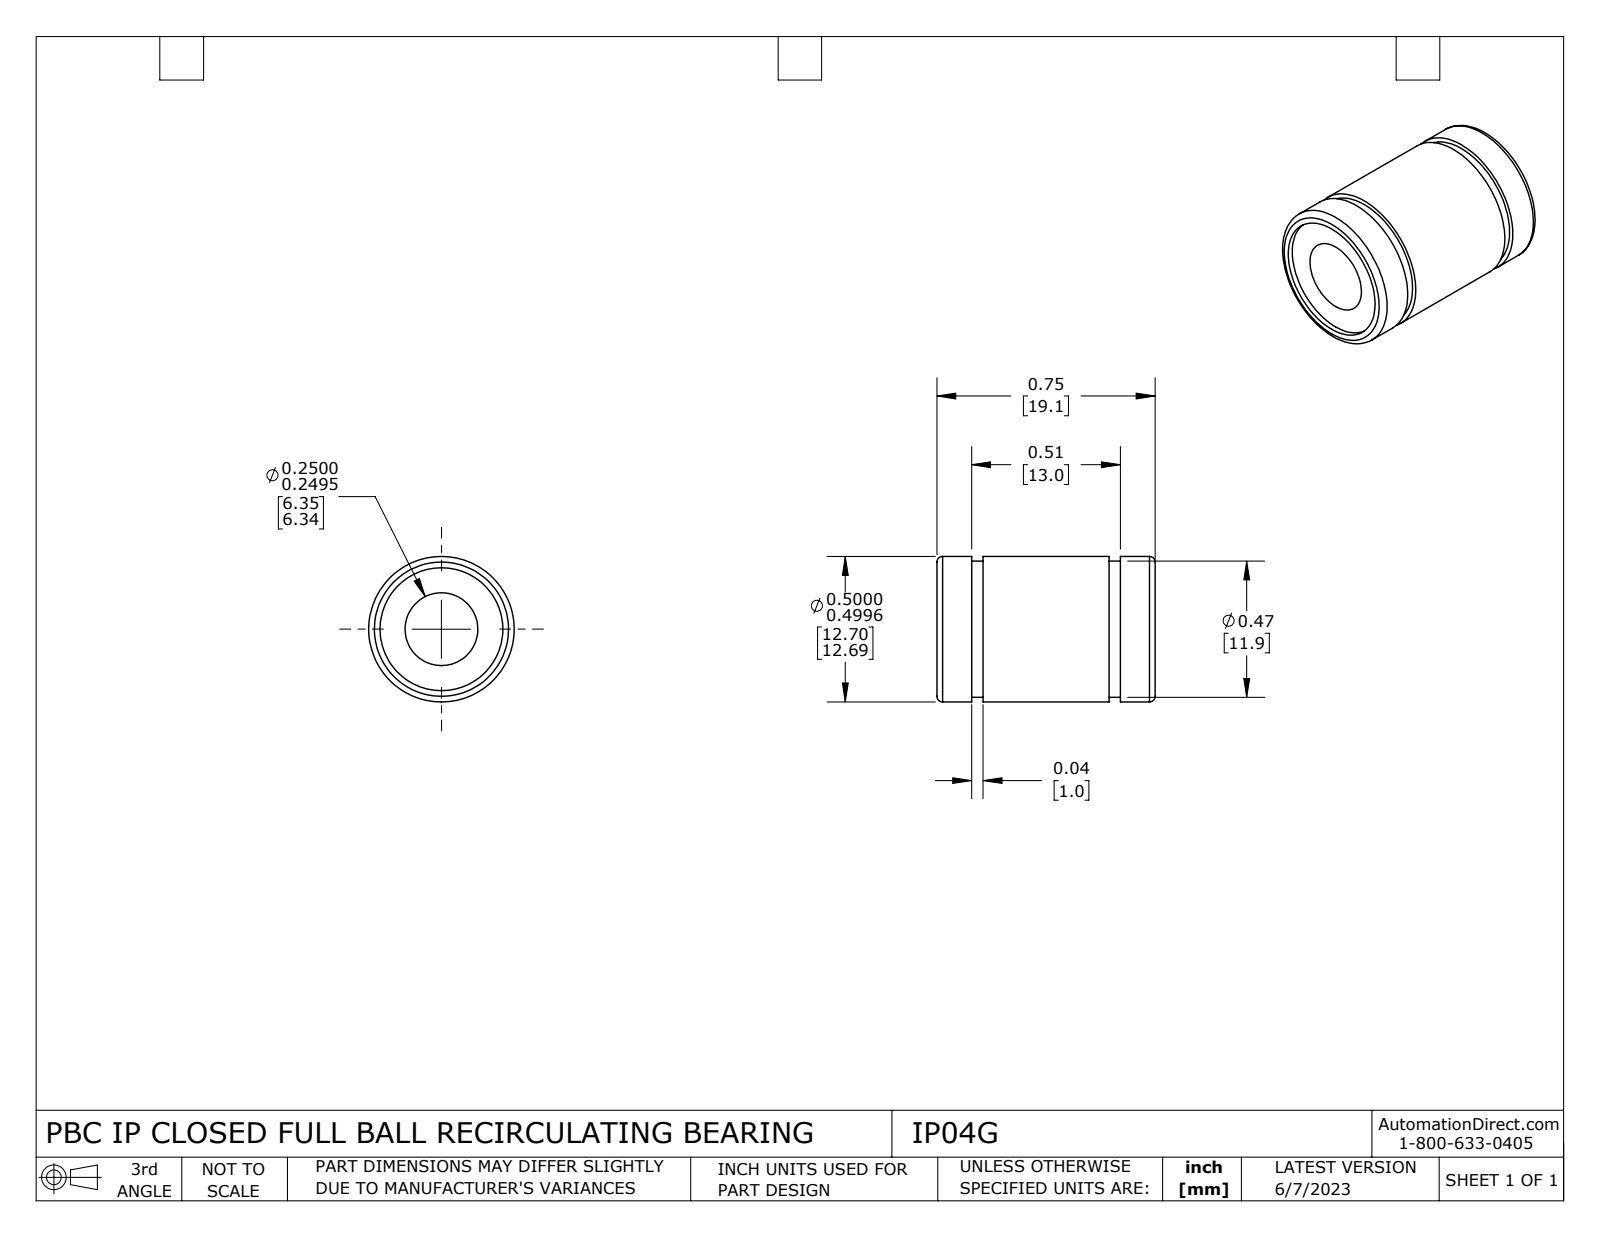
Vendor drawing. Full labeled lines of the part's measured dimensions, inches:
Part name (STEP PRODUCT): IP04G
STEP written by: SolidWorks 2021 (CONFIG_CONTROL_DESIGN)
Units: inches
Bodies: 1 solid, 28 faces (8 planar, 16 cylindrical, 4 other)
Overall size (bounding box): 0.75 × 0.5 × 0.5
Volume: 0.105 in³ · Surface area: 2.144 in²
Round holes (diameter × count): ⌀0.25 ×1, ⌀0.422 ×1
Round bosses / shafts (diameter × count): ⌀0.5 ×1, ⌀0.469 ×1
Main face-to-face distances: 0.711, 0.02, 0.731, 0.12, 0.159, 0.592, 0.631, 0.1, 0.139, 0.572
